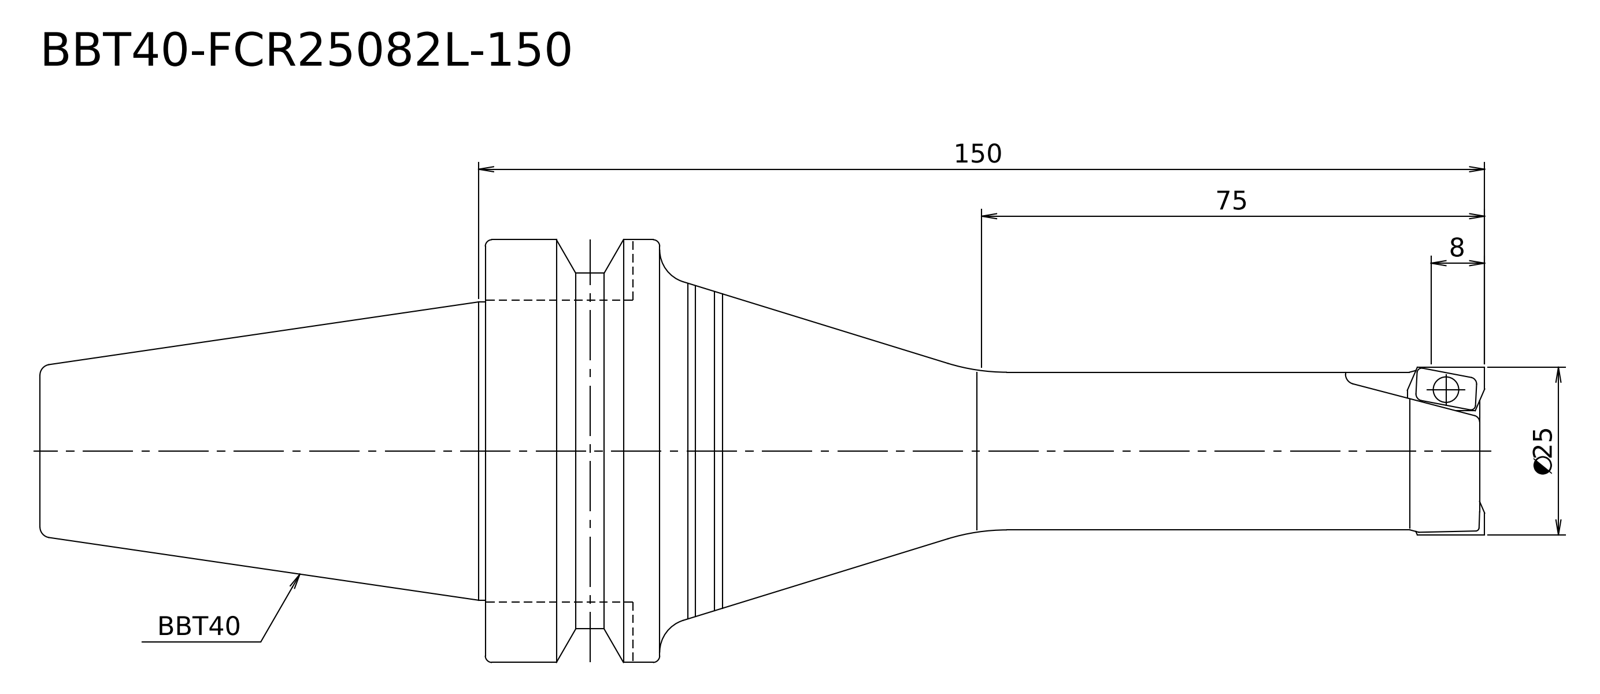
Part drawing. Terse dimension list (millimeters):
written by: Kubotek KeyCreator V8.5.1 (14335) (CONFIG_CONTROL_DESIGN)
unit: mm
bodies: 1 solid, 17 faces (4 planar, 6 cylindrical, 7 other)
size: 215.4 × 63 × 63
volume: 231 327 mm³; area: 28 215 mm²
bosses: 1× ⌀63, 1× ⌀53, 1× ⌀44.45, 1× ⌀25, 1× ⌀23.5
face distances: 66.4, 149, 215.4, 123, 26, 92.4
